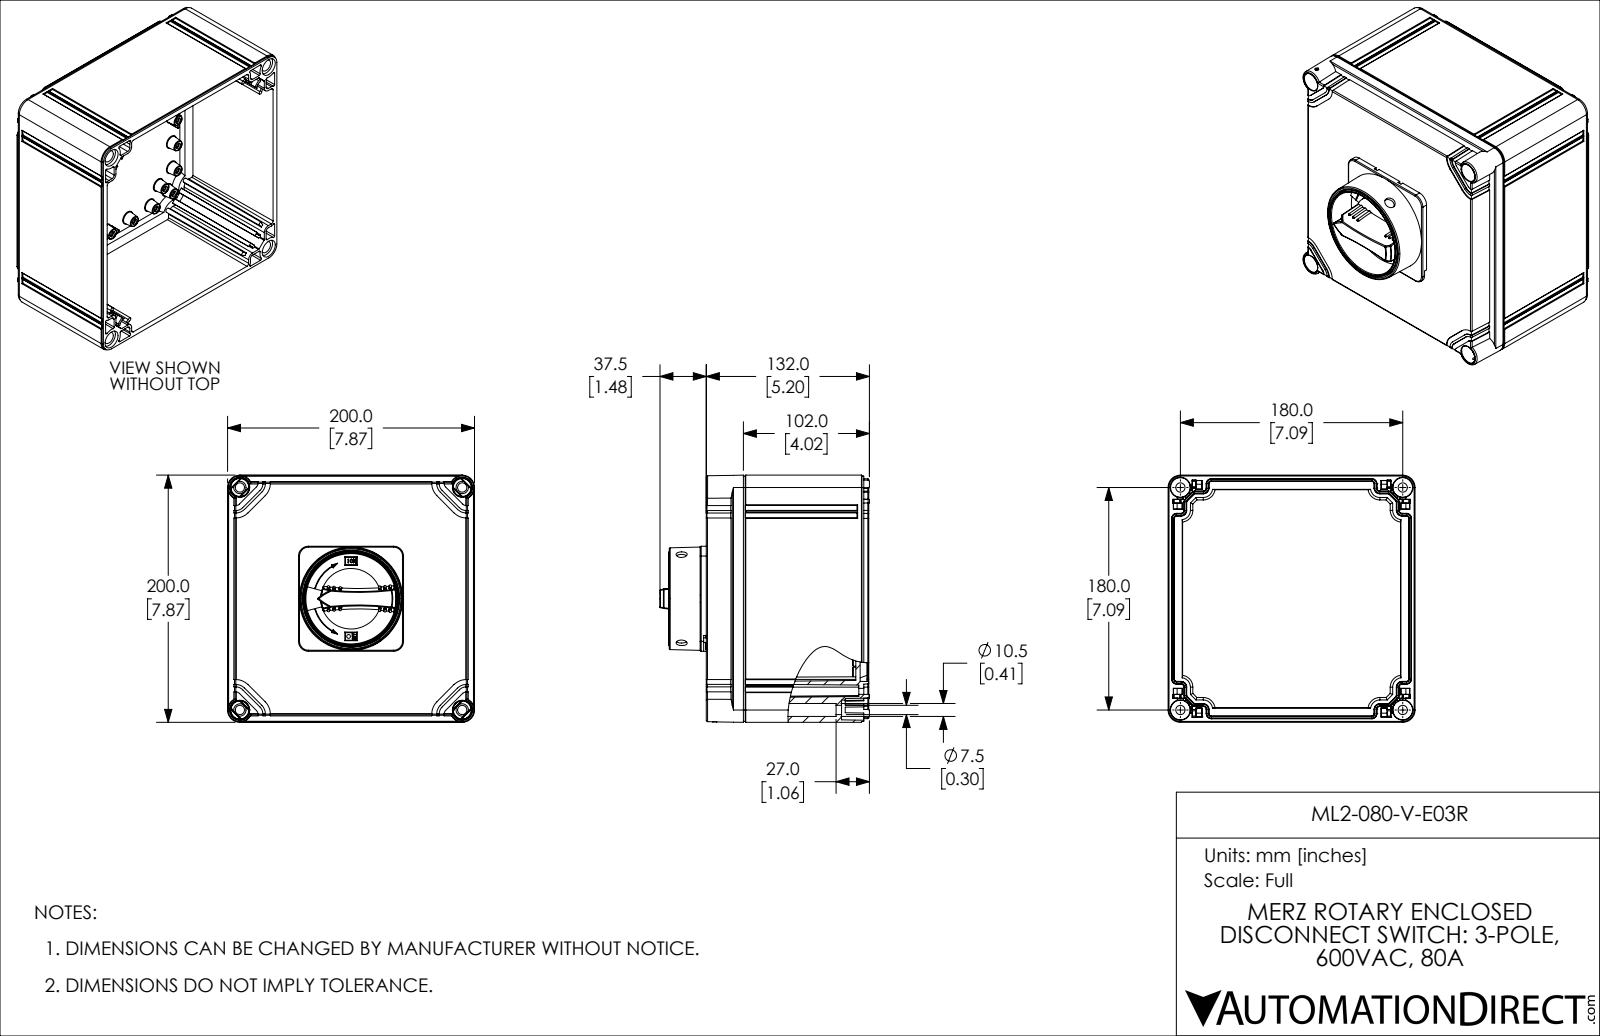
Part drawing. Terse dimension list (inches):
name: ML2-080-V-E03R
written by: SolidWorks 2019 (AUTOMOTIVE_DESIGN)
unit: in
bodies: 3 solids, 2645 faces (1335 planar, 484 cylindrical, 826 other)
size: 7.874 × 7.874 × 6.673
volume: 113.5 in³; area: 758.2 in²
holes: 28× ⌀0.165, 28× ⌀0.197, 4× ⌀0.295, 4× ⌀0.394, 4× ⌀0.413, 2× ⌀0.087, 2× ⌀0.157, 2× ⌀0.354, 1× ⌀0.807, 1× ⌀1.772, 1× ⌀2.878
bosses: 2× ⌀0.315, 1× ⌀3.031, 1× ⌀3.012, 1× ⌀1.929, 1× ⌀1.87, 1× ⌀0.323, 1× ⌀0.15, 1× ⌀0.118
rounds: 60× R0.02, 16× R0.008, 16× R0.039, 16× R0.067, 14× R0.01, 13× R0.315, 12× R0.394, 8× R0.157
face distances: 5.118, 0.138, 1.28, 3.839, 7.874, 3.701, 4.98, 0.217, 0.098, 5.256
hole spacings: 0.984, 5.987, 5.906, 0.71, 0.812, 1.499, 1.682, 1.783
